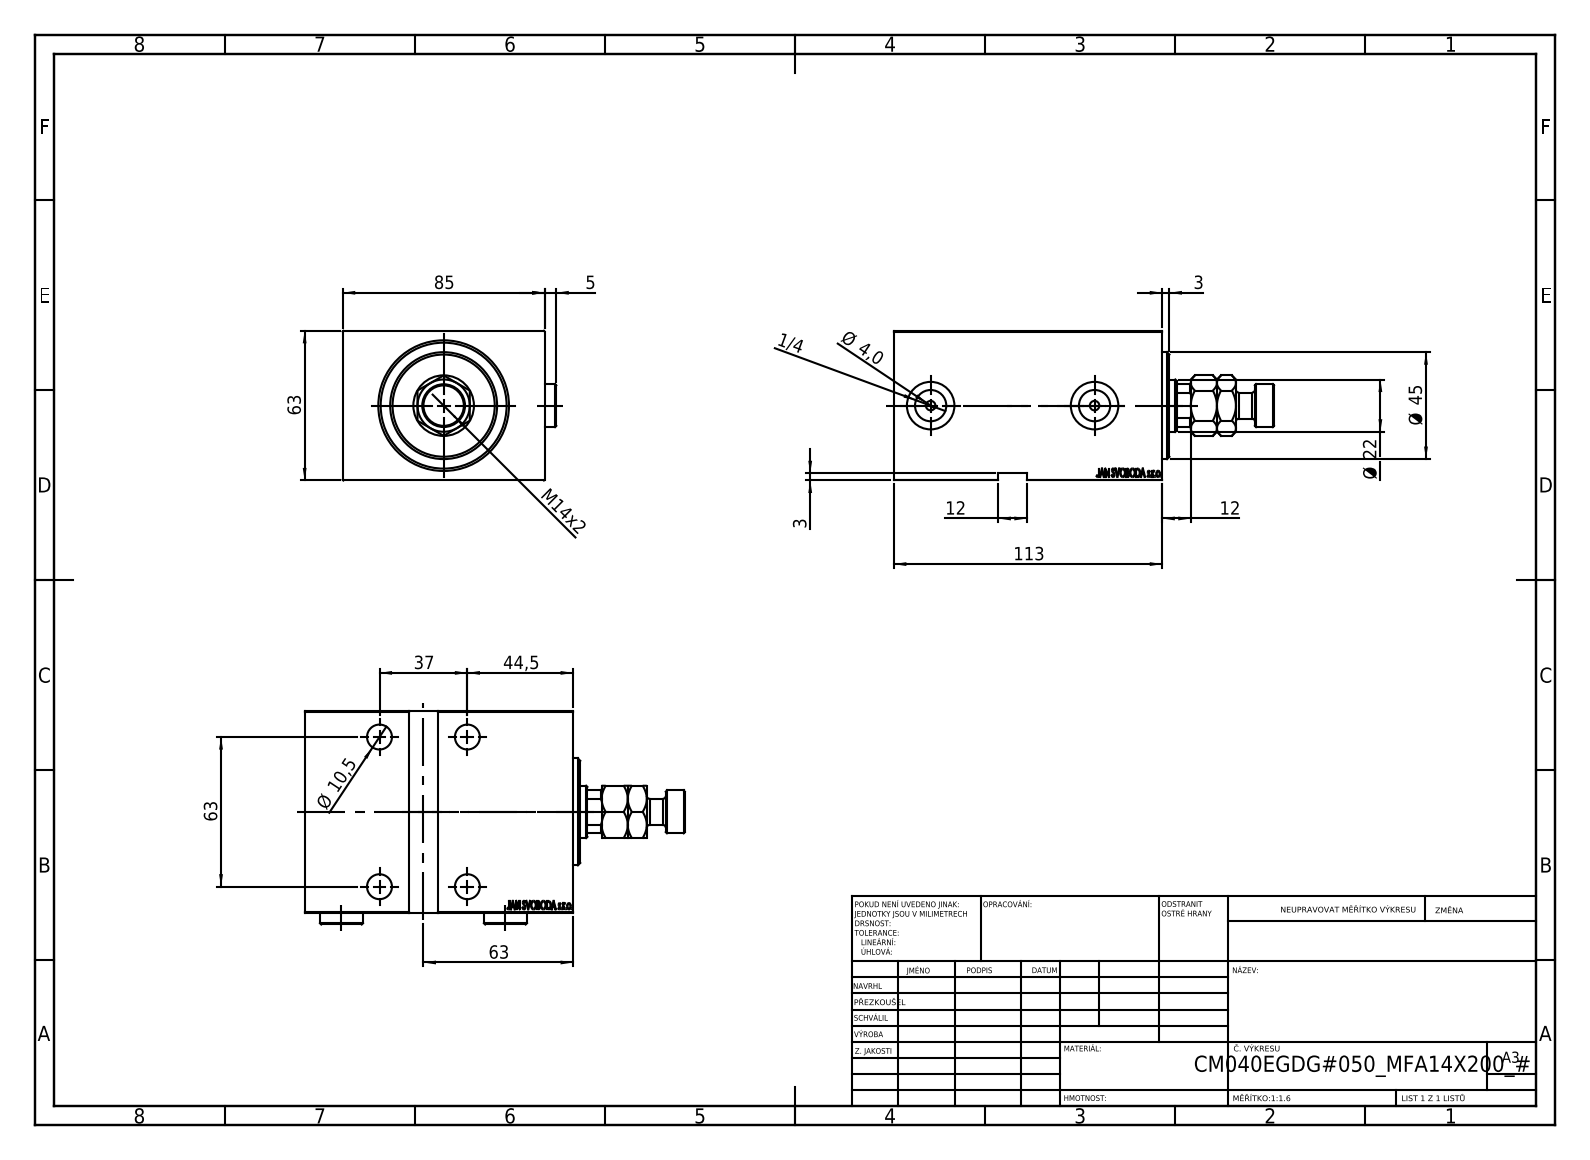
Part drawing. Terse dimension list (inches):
name: V450CM_E_VCP; V450CM_E_Body; Zatka_OIL_PORT; MFA (+1 more)
written by: SolidWorks 2019 (CONFIG_CONTROL_DESIGN)
unit: in
bodies: 6 solids, 964 faces (462 planar, 72 cylindrical, 430 other)
size: 6.299 × 3.539 × 2.48
volume: 33.17 in³; area: 146.9 in²
holes: 4× ⌀0.413, 4× ⌀0.65, 2× ⌀0.157, 2× ⌀0.518, 2× ⌀0.787, 1× ⌀0.492, 1× ⌀0.866, 1× ⌀1.004, 1× ⌀1.575, 1× ⌀2.087
bosses: 3× ⌀0.709, 1× ⌀1.772, 1× ⌀1.654, 1× ⌀0.433
rounds: 1× R0.413
face distances: 2.48, 3.346, 4.449, 0.472, 3.976, 0.197, 0.118, 3.78, 4.252, 2.362
hole spacings: 1.457, 2.48, 2.876, 2.717
